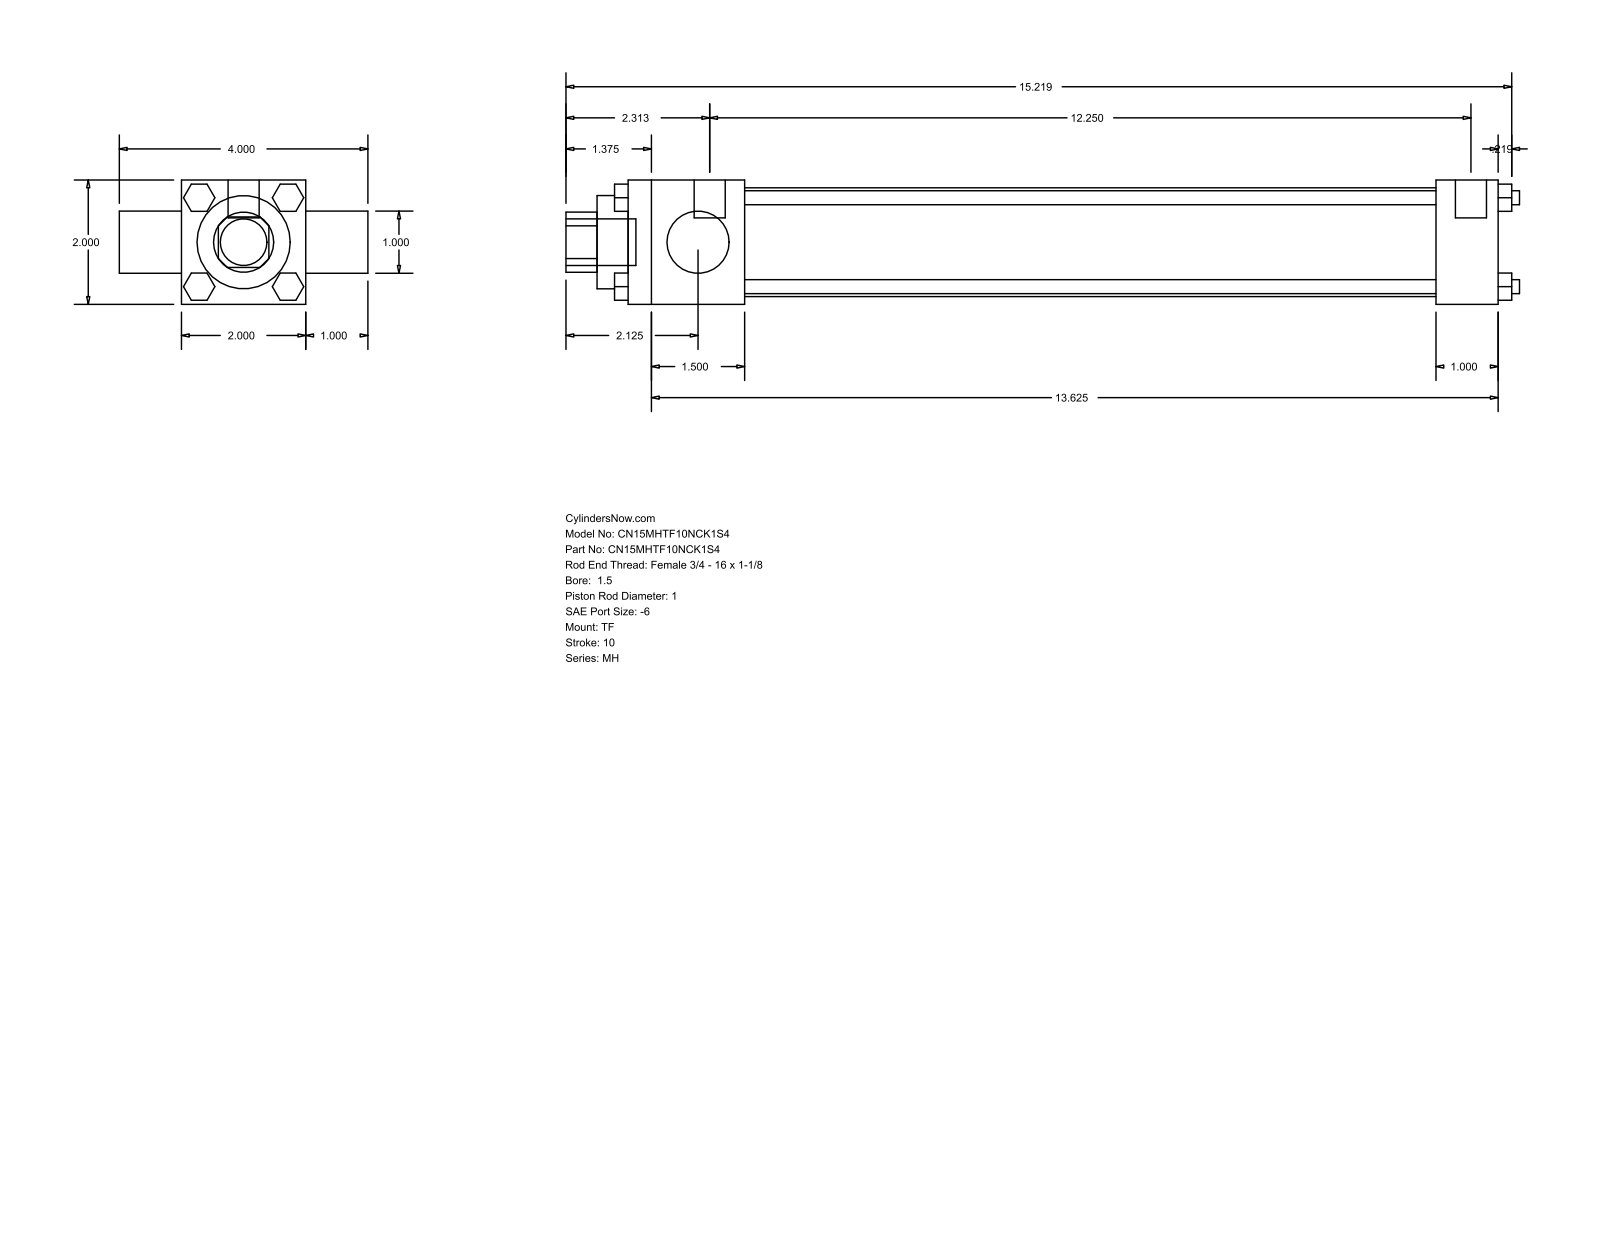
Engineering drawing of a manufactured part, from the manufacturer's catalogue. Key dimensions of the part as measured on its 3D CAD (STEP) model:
Part name (STEP PRODUCT): MH_TF__0150_1
STEP written by: GSSL Pune (CONFIG_CONTROL_DESIGN)
Units: millimetres
Bodies: 0 solids, 120 faces (92 planar, 28 cylindrical, 0 other)
Overall size (bounding box): 389.73 × 101.6 × 50.8
Round holes (diameter × count): ⌀25.4 ×2, ⌀38.1 ×1, ⌀44.45 ×1
Round bosses / shafts (diameter × count): ⌀5.71 ×4, ⌀5.56 ×3, ⌀12.7 ×2, ⌀19.05 ×1
Partial cylindrical surfaces — rounded edges, fillets, slot ends (radius × count): R12.29 ×1
Main face-to-face distances: 50.8, 25.4, 355.6, 76.2, 47.63, 307.97, 330.2, 282.57, 361.16, 12.7
